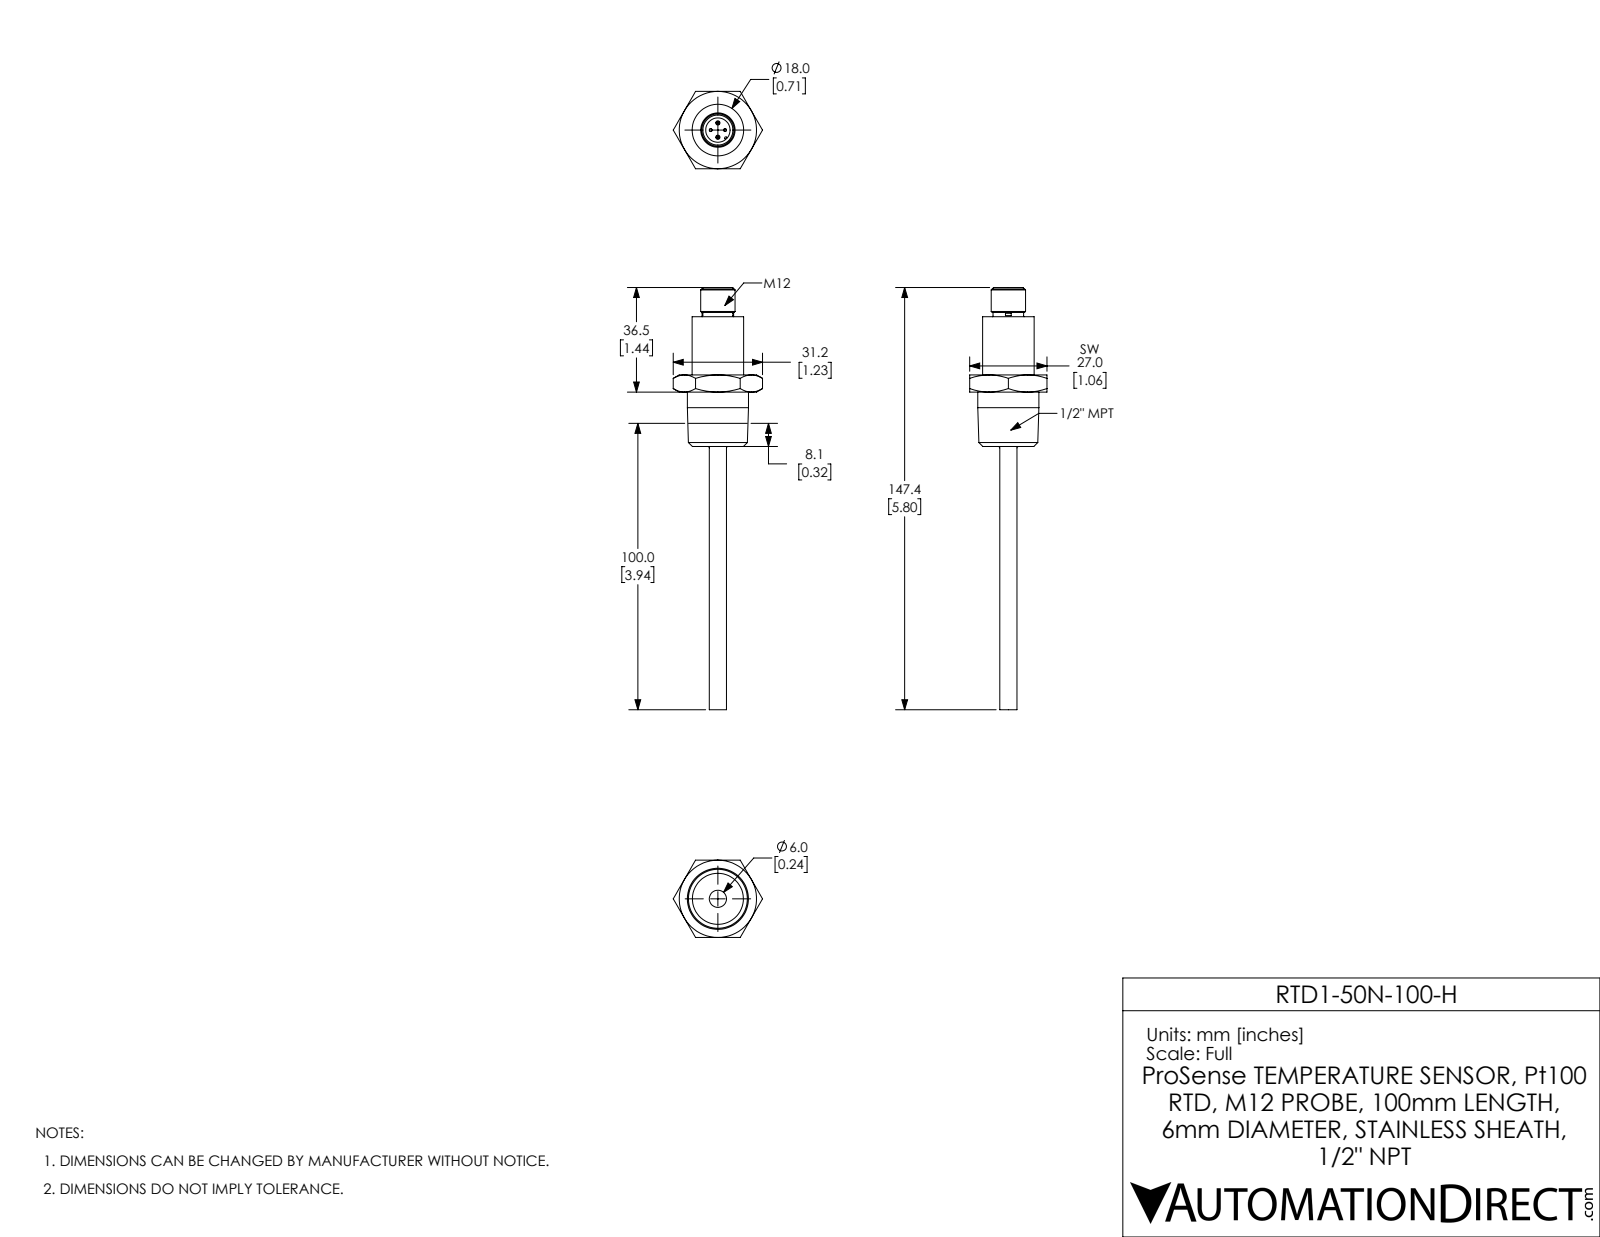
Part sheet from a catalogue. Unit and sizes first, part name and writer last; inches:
Units: inches
Overall size (bounding box): 5.803 × 1.227 × 1.063
Round holes (diameter × count): ⌀0.335 ×1
Round bosses / shafts (diameter × count): ⌀0.04 ×4, ⌀0.84 ×1, ⌀0.709 ×1, ⌀0.472 ×1, ⌀0.421 ×1, ⌀0.413 ×1, ⌀0.236 ×1
Partial cylindrical surfaces — rounded edges, fillets, slot ends (radius × count): R0.016 ×1
Main face-to-face distances: 1.063, 0.236, 0.748, 0.984, 1.783, 1.035, 0.799, 1.831, 1.083, 0.846
Volume: 1.139 in³ · Surface area: 10.11 in²
Bodies: 1 solid, 94 faces (32 planar, 23 cylindrical, 39 other)
Part name (STEP PRODUCT): RTD1-50N-100-H
STEP written by: SolidWorks 2017 (AUTOMOTIVE_DESIGN)
